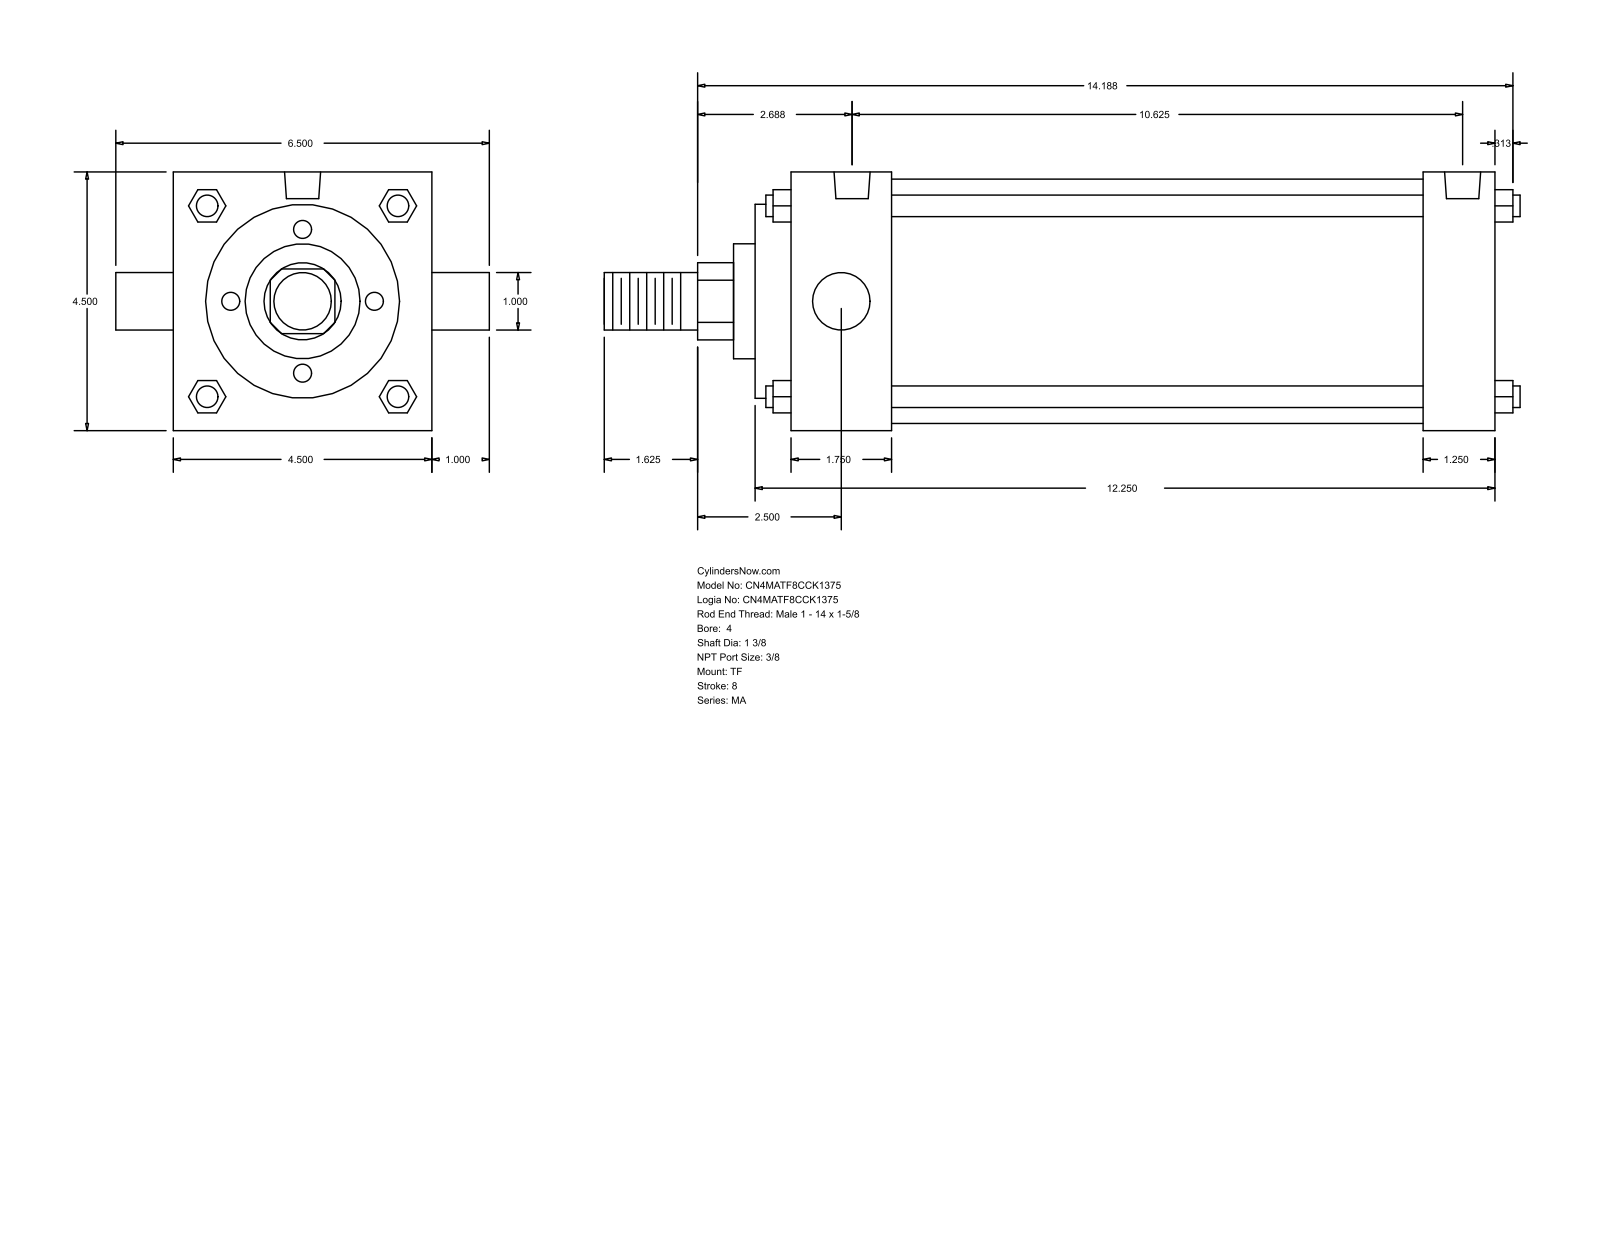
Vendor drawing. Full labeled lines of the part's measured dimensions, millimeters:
Part name (STEP PRODUCT): MA_TF__0400_1.375
STEP written by: GSSL Pune (CONFIG_CONTROL_DESIGN)
Units: millimetres
Bodies: 0 solids, 122 faces (93 planar, 29 cylindrical, 0 other)
Overall size (bounding box): 404.81 × 165.1 × 114.3
Round holes (diameter × count): ⌀11.11 ×3, ⌀15.93 ×2
Round bosses / shafts (diameter × count): ⌀9.53 ×4, ⌀25.4 ×2, ⌀107.95 ×1, ⌀85.72 ×1, ⌀50.8 ×1, ⌀34.92 ×1
Partial cylindrical surfaces — rounded edges, fillets, slot ends (radius × count): R17.06 ×1
Main face-to-face distances: 114.3, 311.16, 15.87, 327.03, 295.28, 279.41, 31.75, 60.32, 44.45, 234.96
Hole centre spacings: 4.76, 4.77, 260.35, 265.11, 265.12, 269.88
